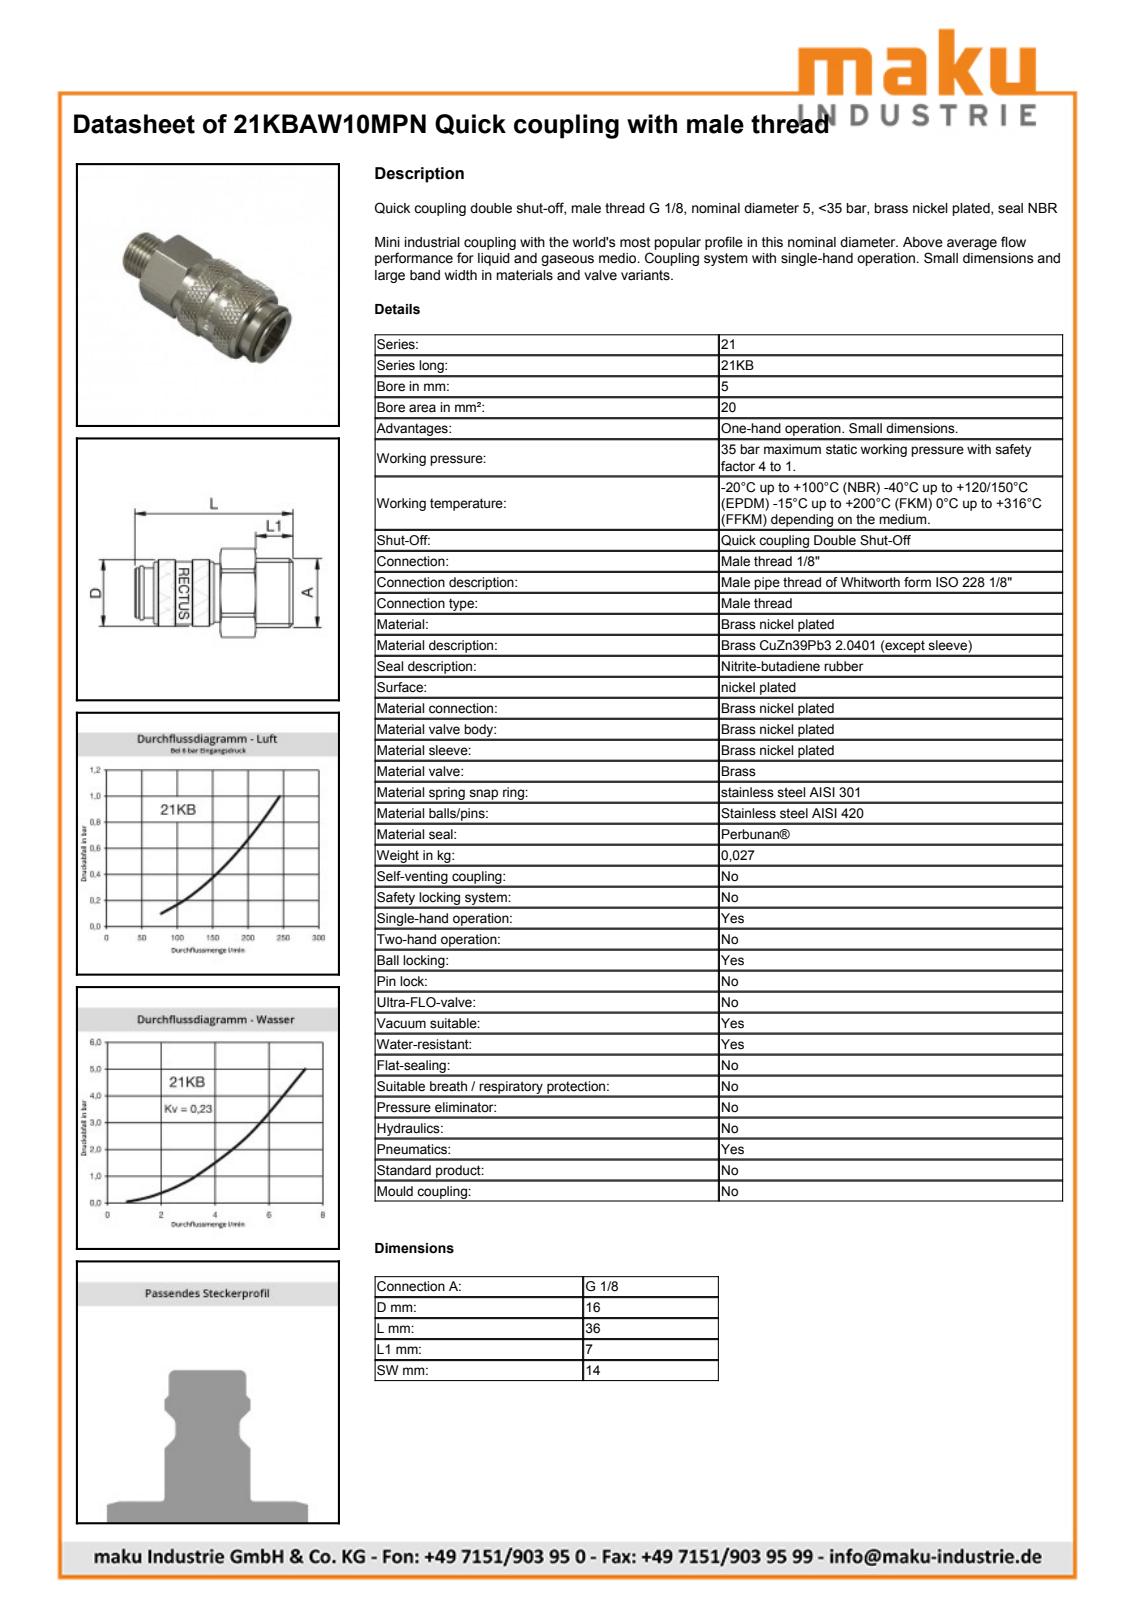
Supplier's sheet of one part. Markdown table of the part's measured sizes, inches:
| quantity | value |
| --- | --- |
| part name | D104955 |
| STEP written by | Autodesk Inventor 2011 (AUTOMOTIVE_DESIGN) |
| units | inches |
| bodies | 2 solids, 453 faces (148 planar, 61 cylindrical, 244 other) |
| overall size | 1.423 × 0.636 × 0.636 |
| volume | 0.318 in³ |
| surface area | 5.237 in² |
| round holes (diameter × count) | 0.478 × 1, 0.551 × 1 |
| round bosses / shafts (diameter × count) | 0.636 × 1, 0.594 × 1, 0.472 × 1, 0.456 × 1, 0.439 × 1, 0.383 × 1 |
| partial cylindrical surfaces (radius × count) | 0.293 × 1, 0.311 × 1 |
| main face-to-face distances | 0.551, 1.148, 1.423, 0.276, 0.636, 0.512, 0.787, 0.177, 0.459, 0.97 |
